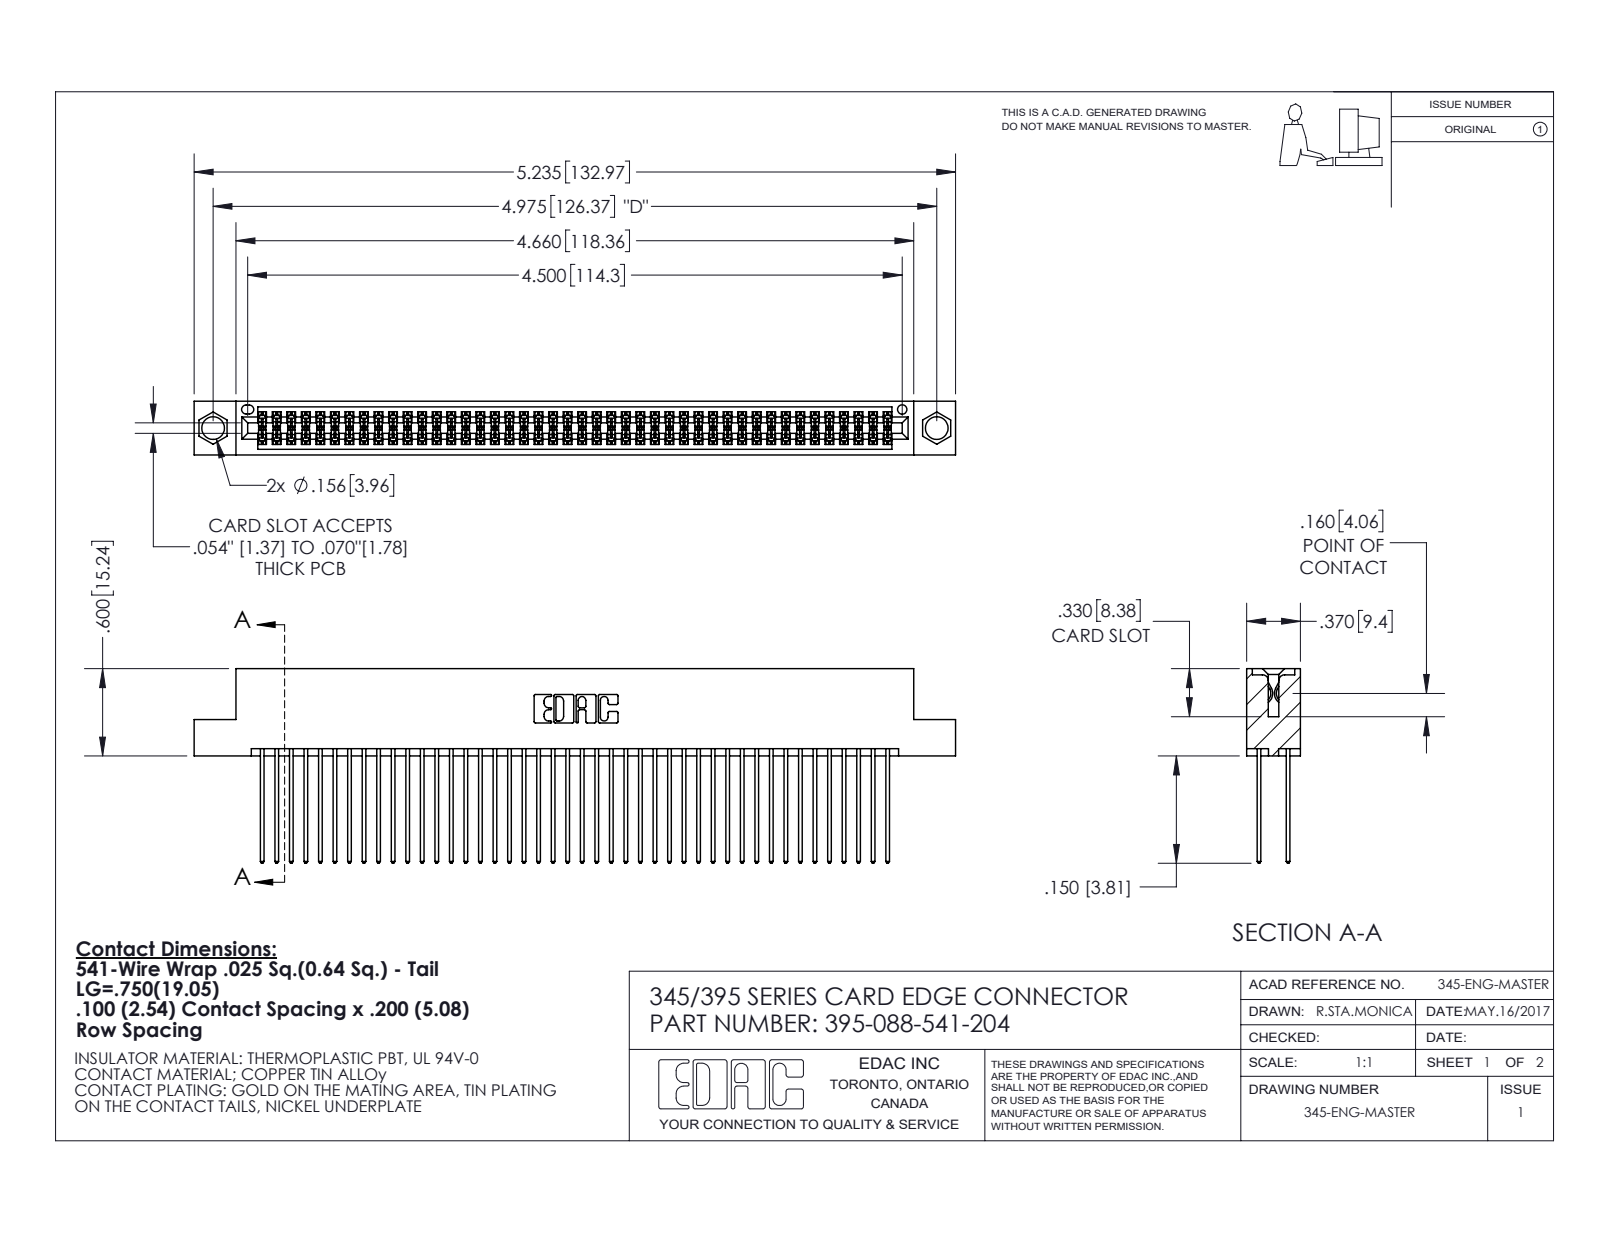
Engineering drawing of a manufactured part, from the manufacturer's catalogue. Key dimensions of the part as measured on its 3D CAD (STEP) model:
Part name (STEP PRODUCT): 345-292-001_345-293-141; 395-088-541-204; 345 Part_Flush Mounting Lugs - 0.156 Dia-TI
STEP written by: SolidWorks 2020 (CONFIG_CONTROL_DESIGN)
Units: inches
Bodies: 89 solids, 4540 faces (2998 planar, 1542 cylindrical, 0 other)
Overall size (bounding box): 5.235 × 1.337 × 0.37
Volume: 0.814 in³ · Surface area: 34.06 in²
Round holes (diameter × count): ⌀0.156 ×2, ⌀0.064 ×1
Partial cylindrical surfaces — rounded edges, fillets, slot ends (radius × count): R0.006 ×175, R0.01 ×88, R0.01 ×22, R0.007 ×6, R0.031 ×6, R0.026 ×3, R0.014 ×2, R0.019 ×2
Main face-to-face distances: 0.072, 0.298, 0.2, 0.098, 0.272, 0.025, 0.225, 0.37, 0.175, 0.149
Hole centre spacings: 0.27, 4.739, 4.975
